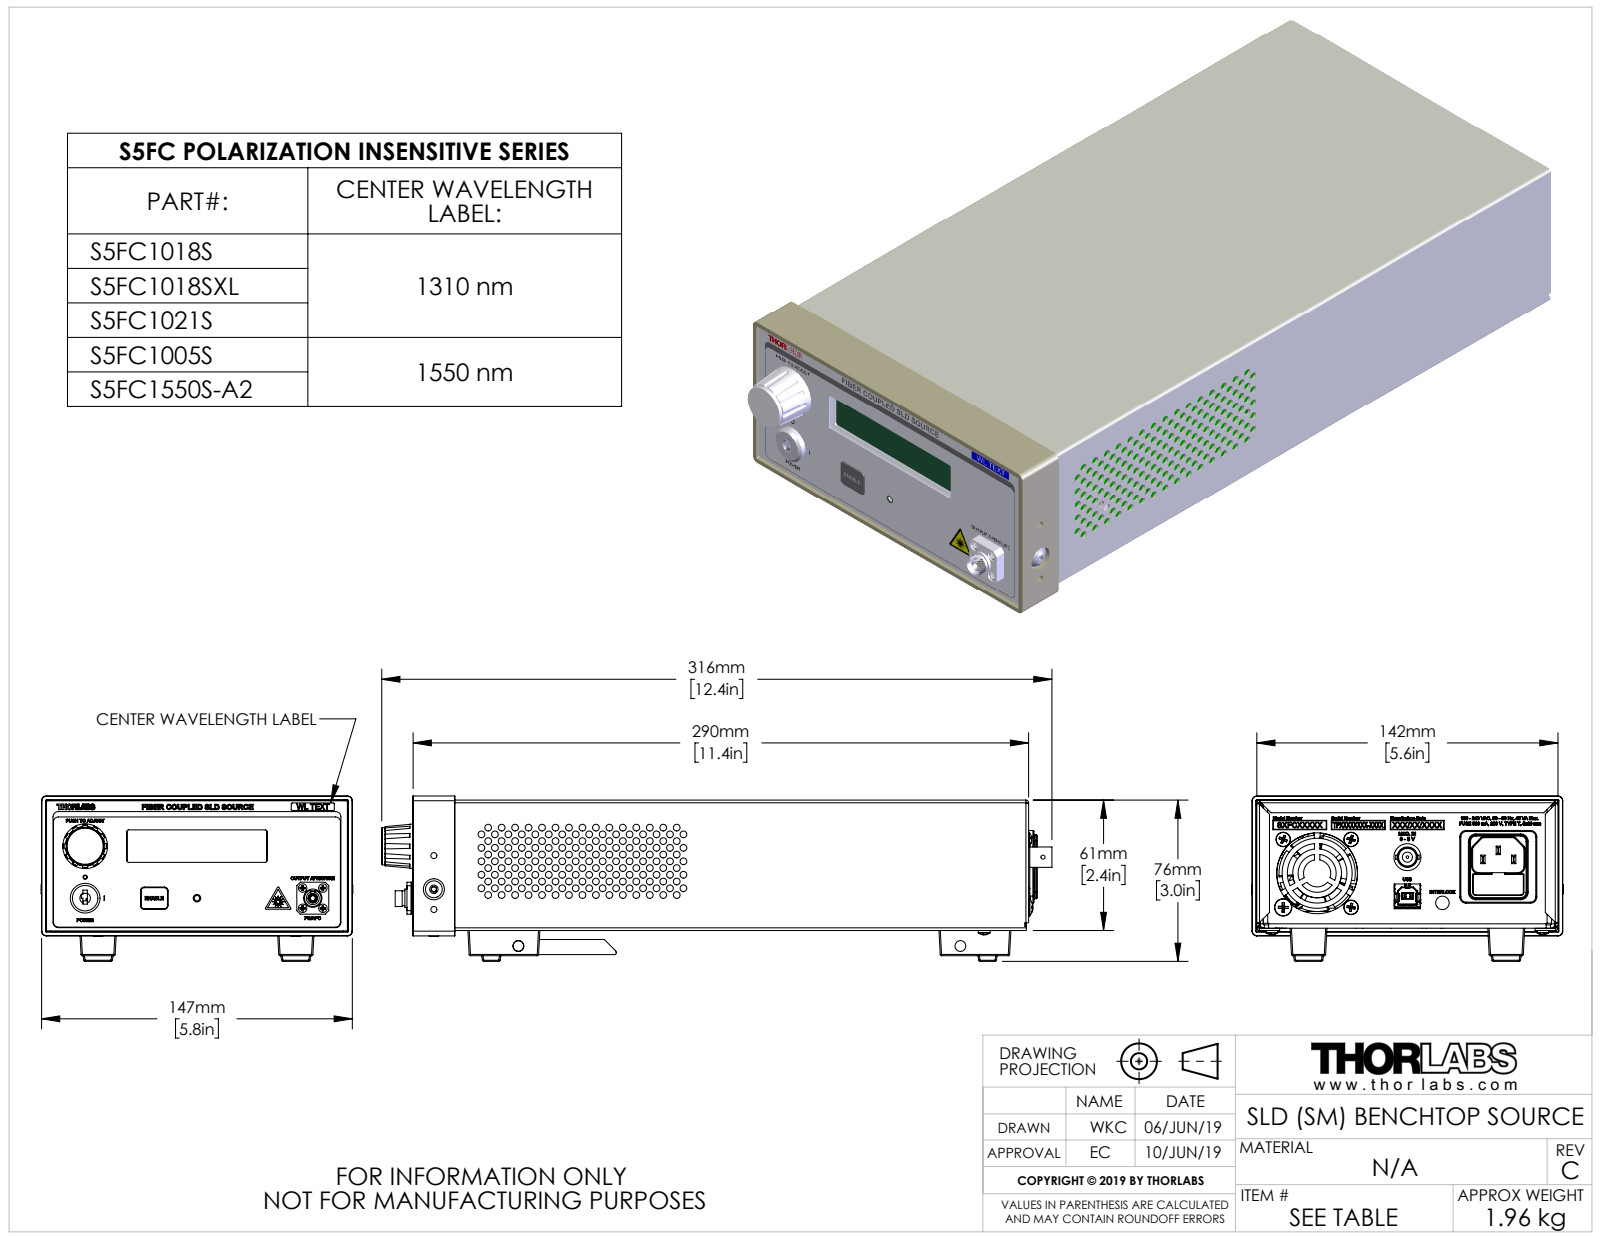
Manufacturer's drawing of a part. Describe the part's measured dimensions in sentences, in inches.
The part is named "TTN027510-E0W". Its 3-D file was written by "SolidWorks 2018 (CONFIG_CONTROL_DESIGN)". It is 0 solids with 12826 faces: 7312 planar, 1186 cylindrical and 4328 other. Overall it measures 12.44 by 5.786 by 3.069 inches. Round holes: 170 of diameter 0.125, 44 of diameter 0.037, 16 of diameter 0.039, 16 of diameter 0.04, 14 of diameter 0.032, 8 of diameter 0.07, 8 of diameter 0.104, 8 of diameter 0.12, 8 of diameter 0.122, 8 of diameter 0.157, 7 of diameter 0.14, 7 of diameter 0.165. Round bosses or shafts: 9 of diameter 0.15, 8 of diameter 0.165, 8 of diameter 0.12, 6 of diameter 0.138, 6 of diameter 0.018, 5 of diameter 0.27, 5 of diameter 0.164, 4 of diameter 0.312. Partial cylindrical surfaces (rounded edges, fillets, slot ends): 51 of radius 0.02, 48 of radius 0.025, 32 of radius 0.005, 20 of radius 0.01, 15 of radius 0.01, 14 of radius 0.118, 13 of radius 0.05, 9 of radius 0.02. The main face-to-face distances are 0.04, 0.062, 2.378, 0.25, 2.338, 2.276, 2.315, 0.312, 2.026, 2.065. The hole center spacings are 0.5, 1.25, 0.25, 1, 0.75, 1.031, 1.118, 1.5.
